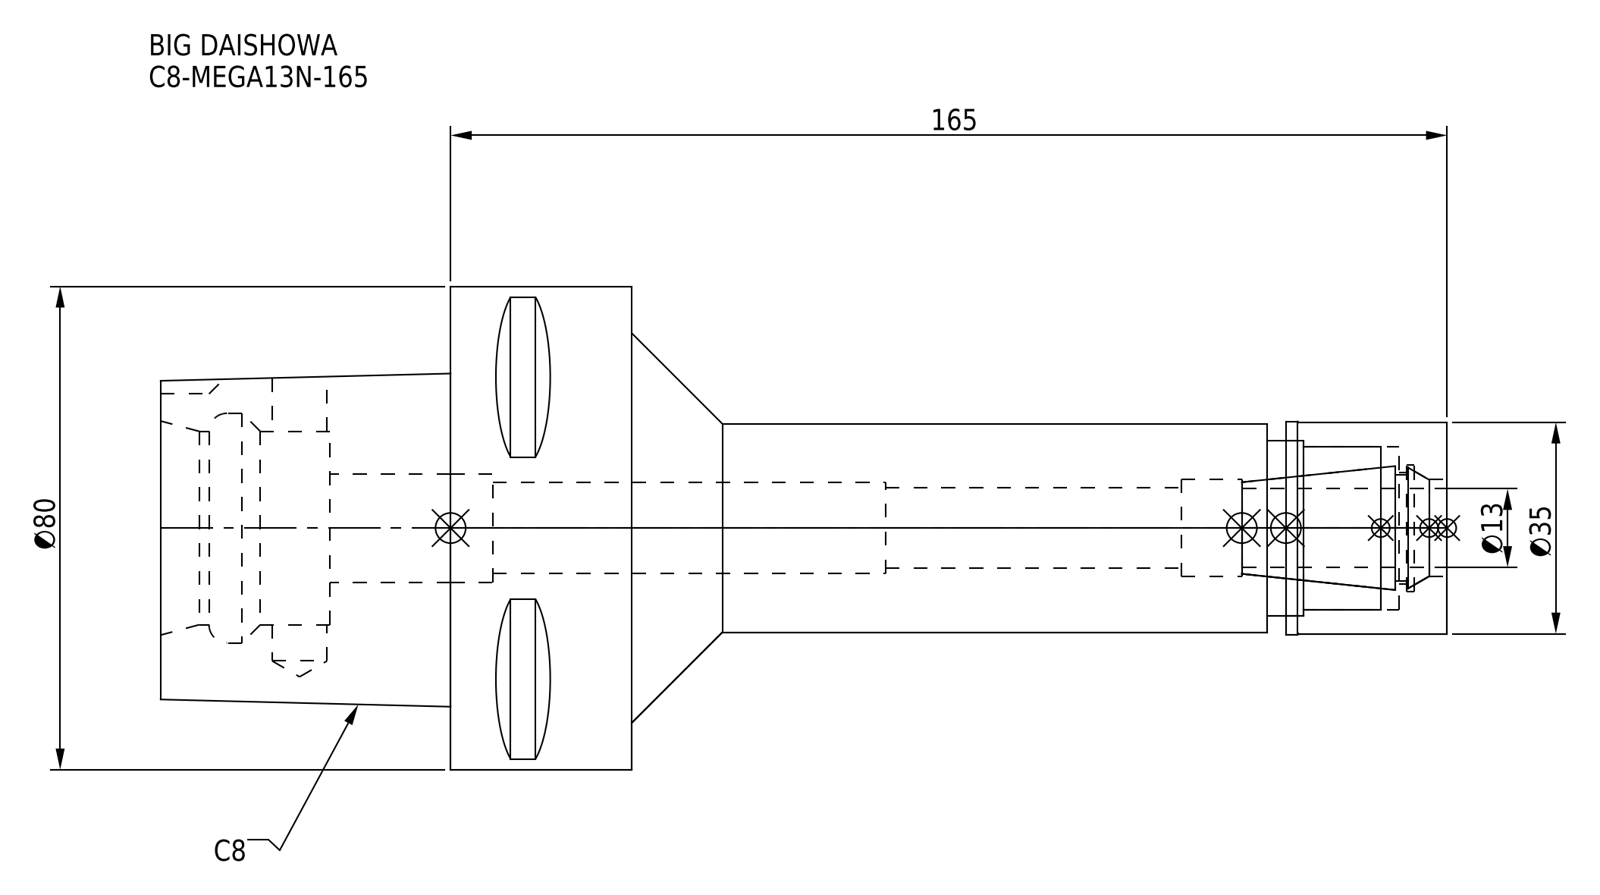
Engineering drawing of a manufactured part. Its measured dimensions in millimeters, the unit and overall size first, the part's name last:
Units: millimetres
Overall size (bounding box): 213 × 80 × 80
Round holes (diameter × count): ⌀9.1 ×1, ⌀13.3 ×1, ⌀15 ×1, ⌀16 ×1, ⌀18 ×1, ⌀18.5 ×1, ⌀21 ×1, ⌀27 ×1, ⌀29 ×1, ⌀32 ×1, ⌀38 ×1
Round bosses / shafts (diameter × count): ⌀80 ×1, ⌀35.3 ×1, ⌀35 ×1, ⌀34.5 ×1
Partial cylindrical surfaces — rounded edges, fillets, slot ends (radius × count): R6 ×1
Main face-to-face distances: 30, 78, 48, 135, 165, 213, 20, 185, 50, 28
Volume: 335 399 mm³ · Surface area: 56 554 mm²
Bodies: 2 solids, 98 faces (39 planar, 41 cylindrical, 18 other)
Part name (STEP PRODUCT): C8-MEGA13N-165-130-FreeParts; C8-MEGA13N-165_1.stp; DXF_TEMP_ASSY_ASM_4_ASM.stp; MGN13_1.stp (+3 more)
STEP written by: SolidWorks 2019 (CONFIG_CONTROL_DESIGN)
